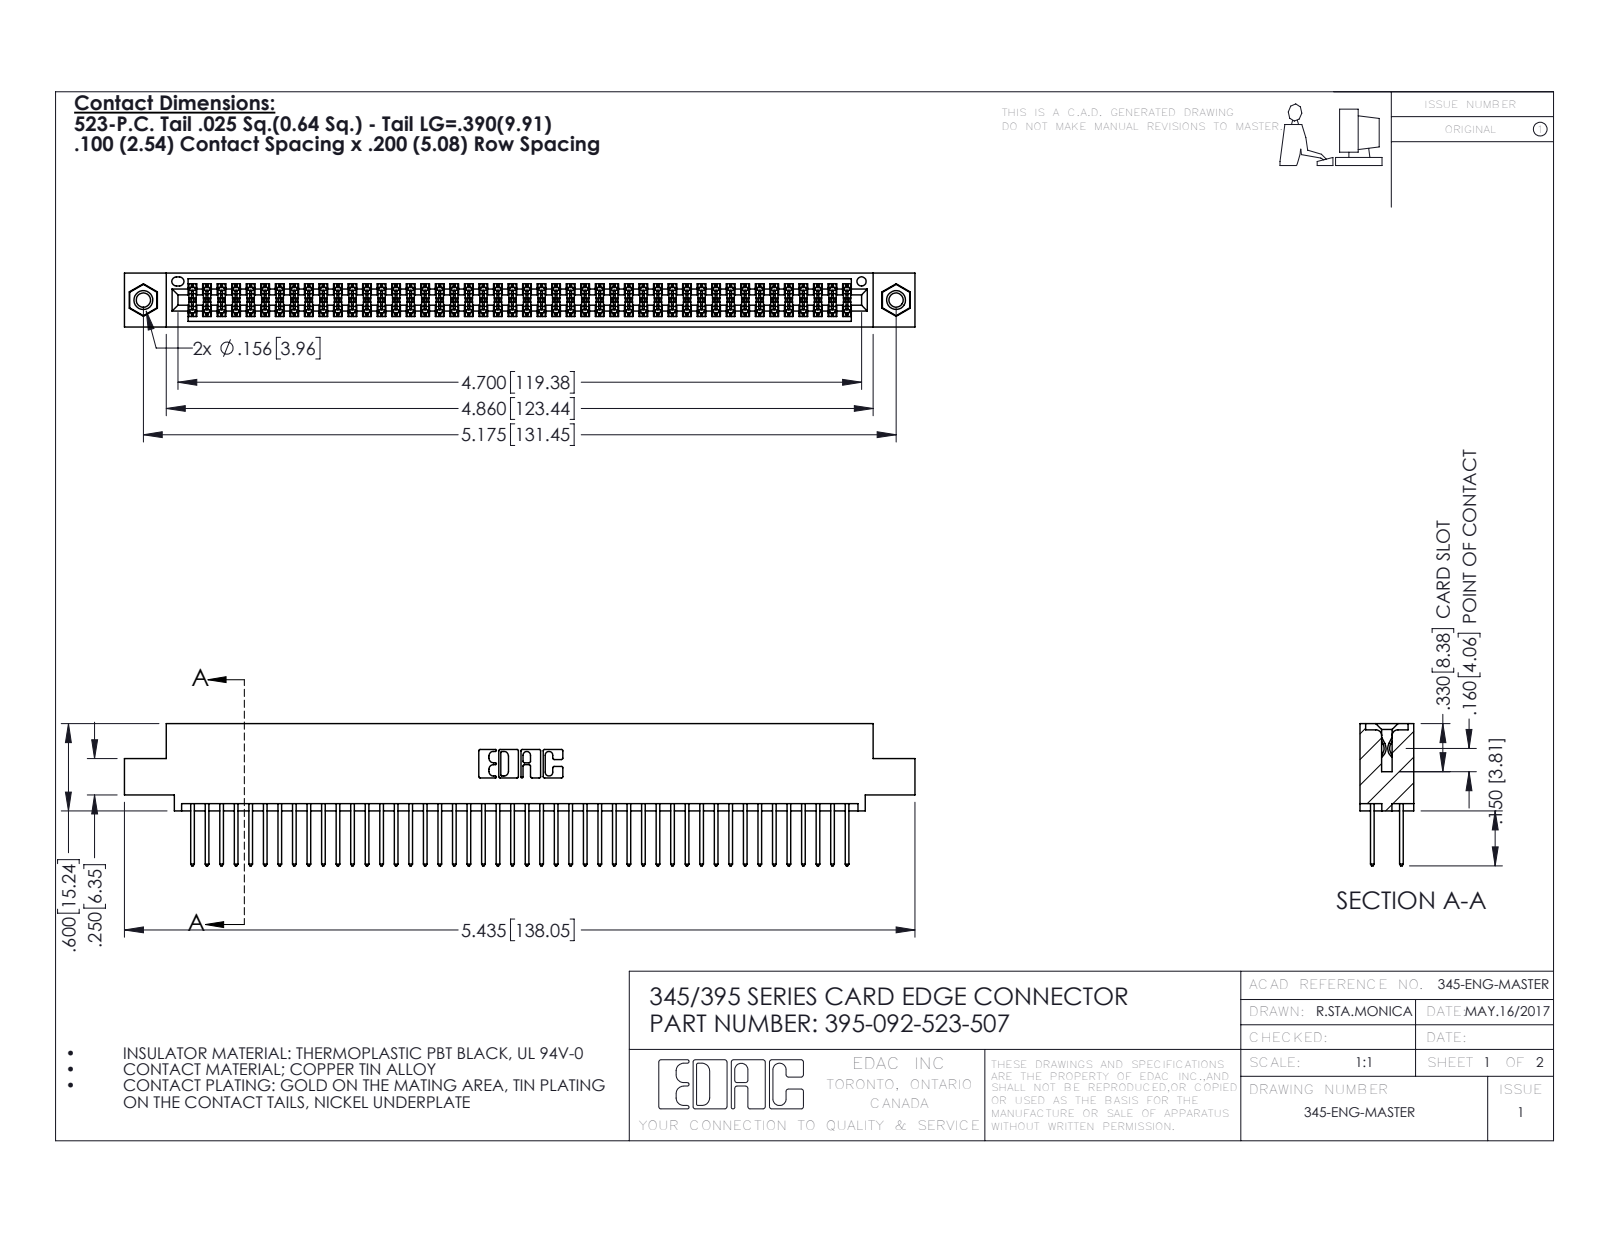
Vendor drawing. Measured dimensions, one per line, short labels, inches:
name: 345-292-001_345-293-123; 345 Part_0.110 Offset - 0.156 Dia-TI; 345-250-001_345-250-005-103; 395-092-523-507
written by: SolidWorks 2016 (CONFIG_CONTROL_DESIGN)
unit: in
bodies: 95 solids, 4790 faces (3152 planar, 1622 cylindrical, 16 other)
size: 5.435 × 0.977 × 0.37
volume: 0.827 in³; area: 32.66 in²
holes: 2× ⌀0.098, 2× ⌀0.125, 2× ⌀0.156, 1× ⌀0.064
bosses: 2× ⌀0.155
rounds: 138× R0.006, 92× R0.01, 22× R0.01, 6× R0.007, 6× R0.031, 3× R0.026, 2× R0.014, 2× R0.019
face distances: 0.072, 0.298, 0.2, 0.098, 0.272, 0.025, 0.37, 0.225, 0.175, 0.149
hole spacings: 0.27, 4.939, 5.175
